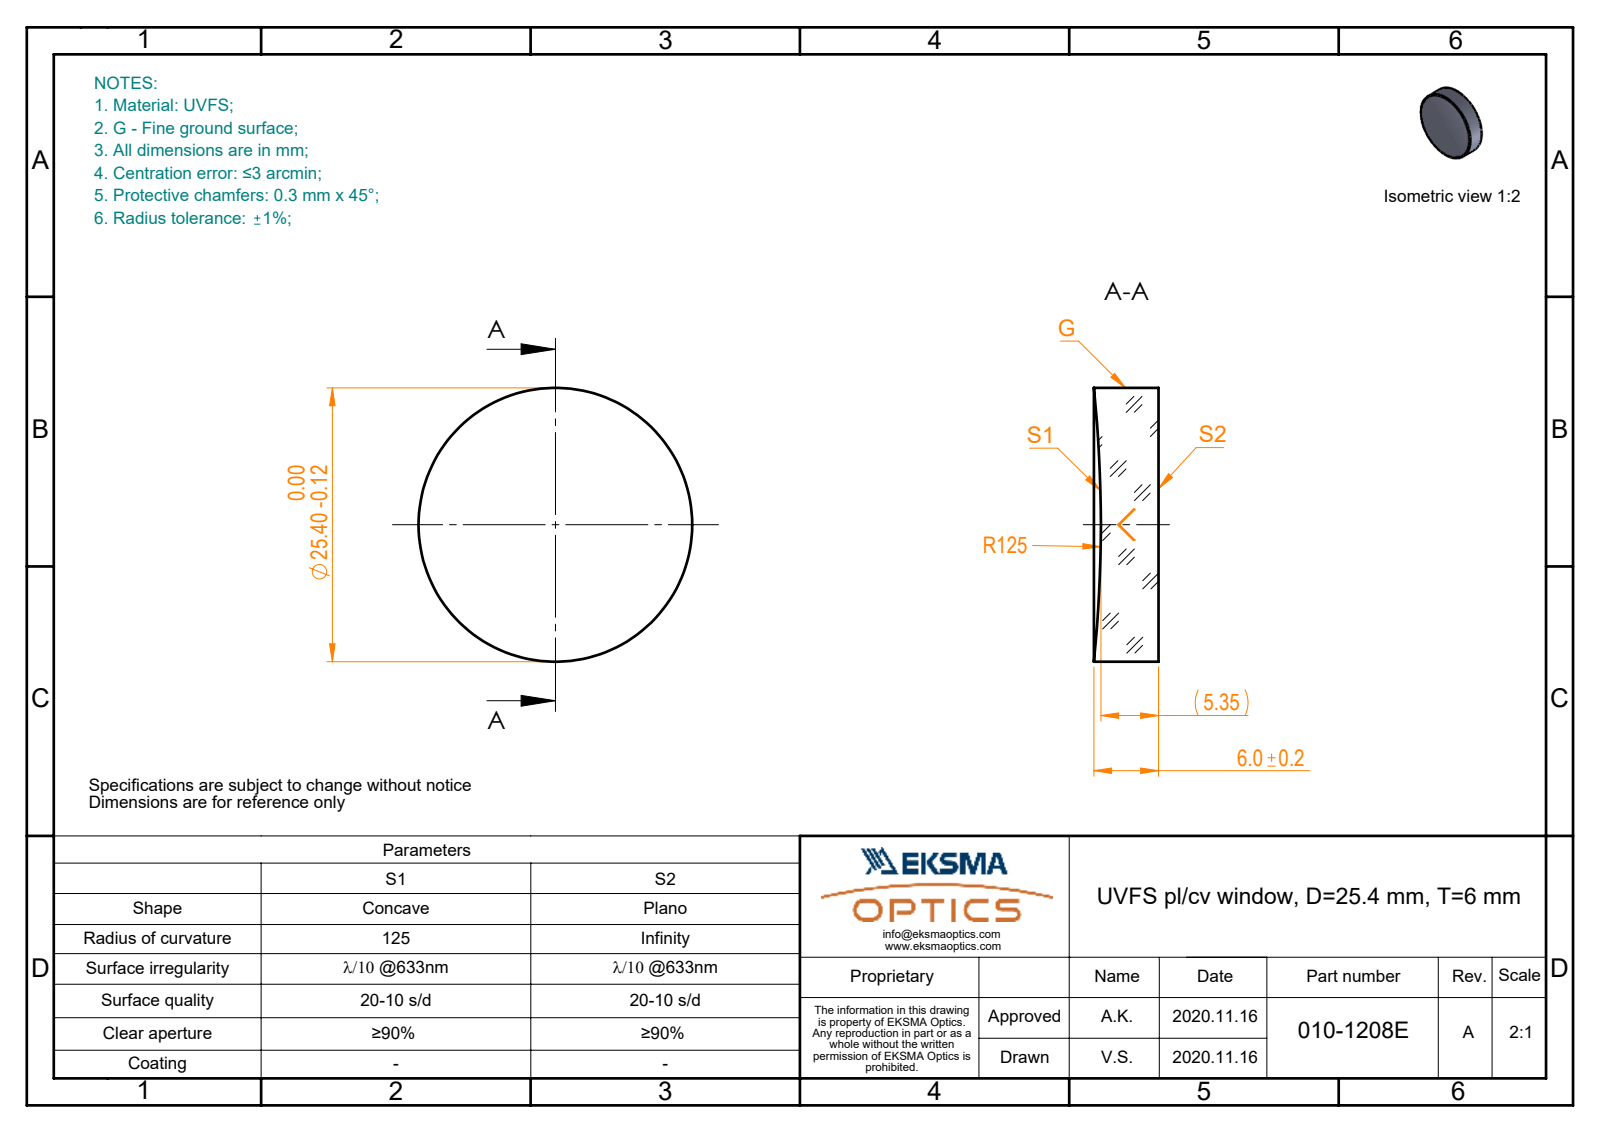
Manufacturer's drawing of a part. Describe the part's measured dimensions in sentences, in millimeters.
The part is named "010-1208E_UVFS_PCV_window". Its 3-D file was written by "SolidWorks 2019 (CONFIG_CONTROL_DESIGN)". It is 1 solid with 5 faces: 1 planar, 2 cylindrical and 2 other. Overall it measures 25.4 by 25.4 by 6 millimeters. Its volume is 2 876 cubic millimeters and its surface area 1 494 square millimeters. Round bosses or shafts: 1 of diameter 25.4.
